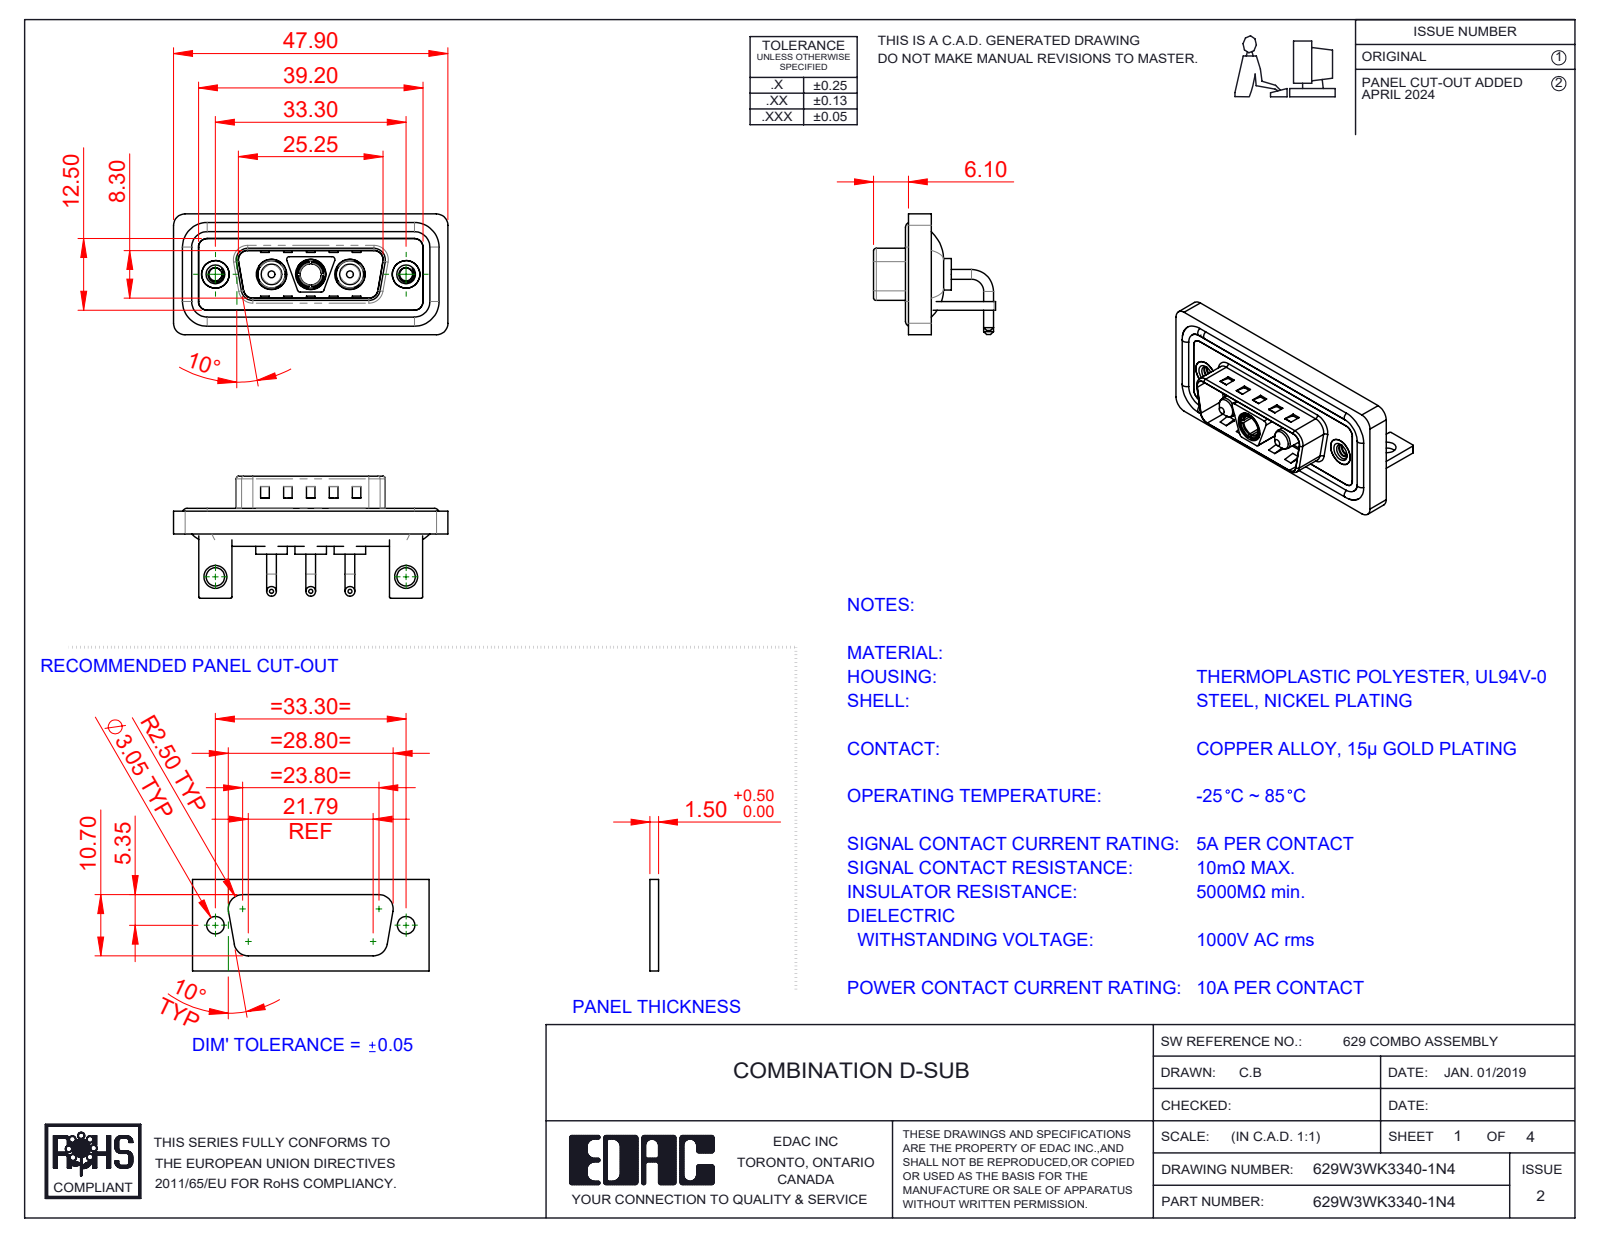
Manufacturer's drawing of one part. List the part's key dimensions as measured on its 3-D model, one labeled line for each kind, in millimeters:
Part name (STEP PRODUCT): 629Combo Waterproof Housing_15 Contacts; 629Combo Stabilizer Bracket; Power Socket_10A RA; 629Combo Shell Rear_15 Contacts (+5 more)
STEP written by: SolidWorks 2023 (CONFIG_CONTROL_DESIGN)
Units: millimetres
Bodies: 15 solids, 661 faces (251 planar, 274 cylindrical, 136 other)
Overall size (bounding box): 47.9 × 21.3 × 21.1
Volume: 5 986 mm³ · Surface area: 9 848 mm²
Round holes (diameter × count): ⌀4.85 ×3, ⌀5.3 ×3, ⌀2.26 ×2, ⌀3.2 ×2, ⌀4 ×2, ⌀4.8 ×2, ⌀5 ×2, ⌀3.7 ×1
Round bosses / shafts (diameter × count): ⌀1.7 ×6, ⌀1.6 ×4, ⌀5.5 ×3, ⌀5.2 ×3, ⌀4.75 ×3, ⌀3.75 ×3, ⌀4.9 ×2, ⌀3.6 ×2
Partial cylindrical surfaces — rounded edges, fillets, slot ends (radius × count): R2 ×21, R1.5 ×18, R0.25 ×16, R0.5 ×13, R1.6 ×8, R0.6 ×4, R0.65 ×4, R0.9 ×4
Main face-to-face distances: 0.4, 1.5, 0.8, 2.9, 1.1, 2.1, 3.7, 1.6, 1.2, 4.5
Hole centre spacings: 6.85, 9.8, 16.65, 23.5, 33.3, 13.7
